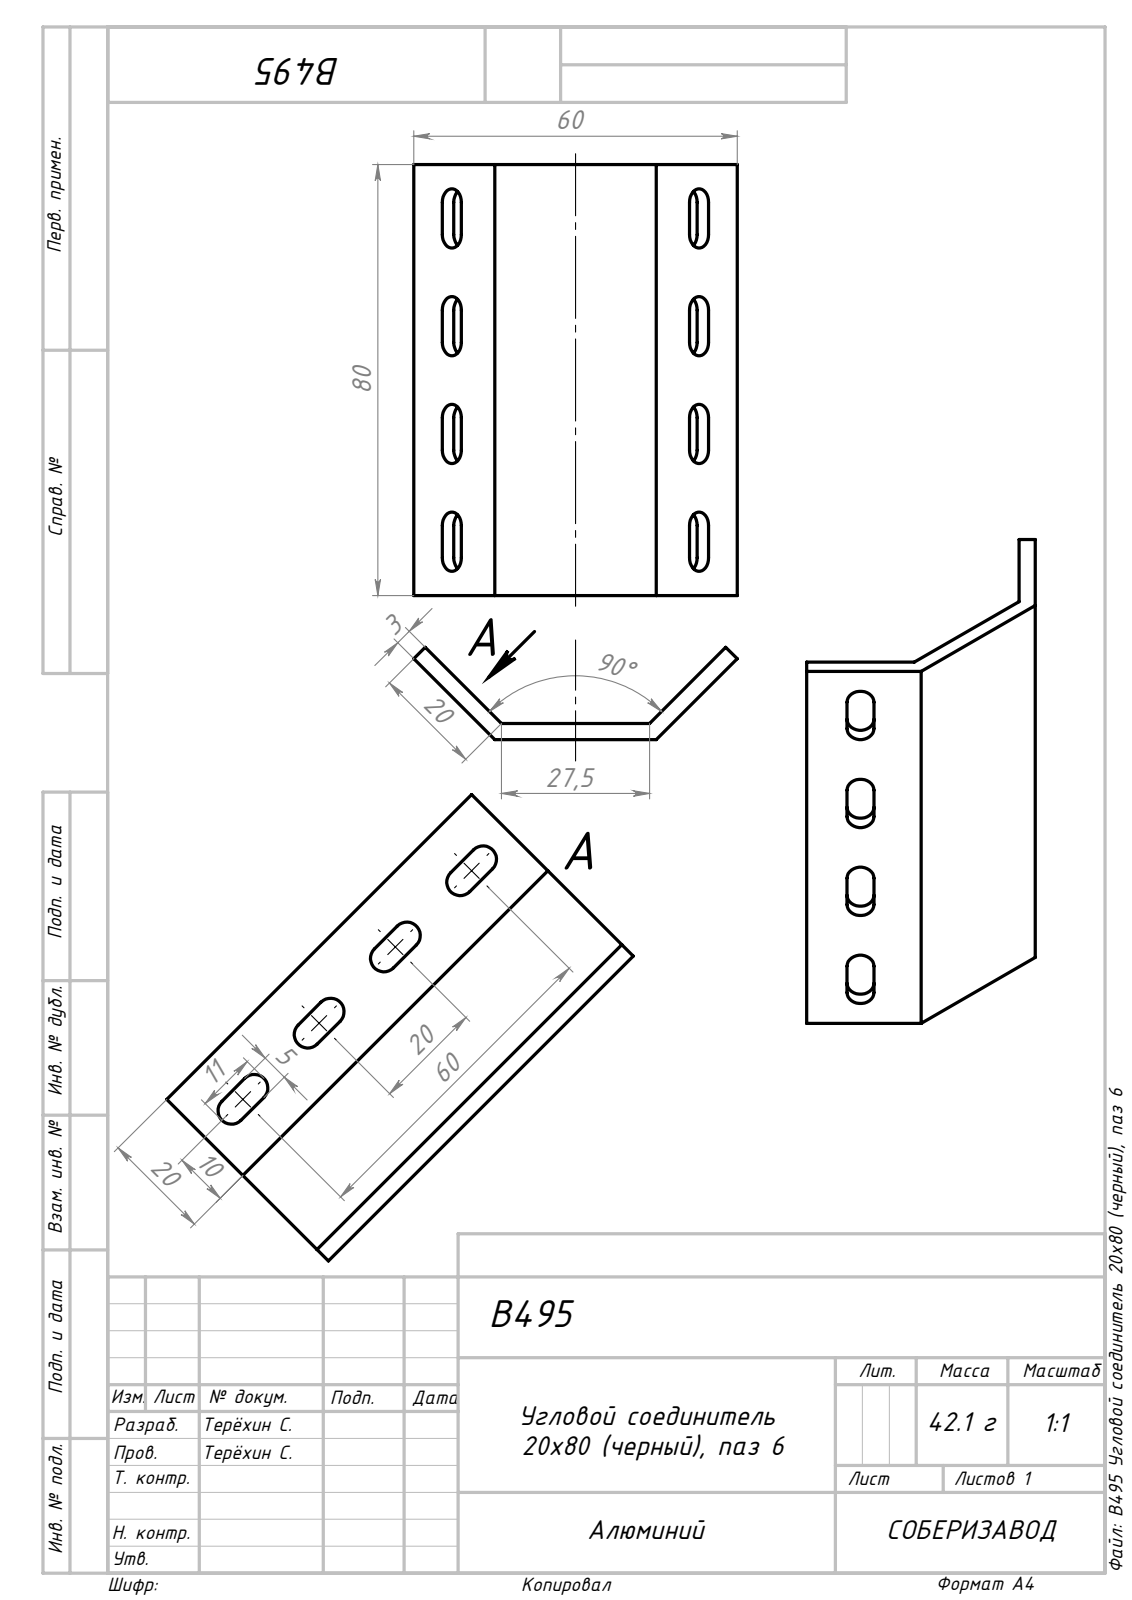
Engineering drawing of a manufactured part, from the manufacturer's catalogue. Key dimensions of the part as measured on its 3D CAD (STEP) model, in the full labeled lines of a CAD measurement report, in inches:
Part name (STEP PRODUCT): B495 Угловой соединитель 20x80 (черный), паз 6_00; Сборка2
STEP written by: SolidWorks 2022 (AUTOMOTIVE_DESIGN)
Units: inches
Bodies: 1 solid, 42 faces (26 planar, 16 cylindrical, 0 other)
Overall size (bounding box): 3.15 × 2.362 × 0.675
Volume: 0.952 in³ · Surface area: 18.54 in²
Partial cylindrical surfaces — rounded edges, fillets, slot ends (radius × count): R0.098 ×16
Main face-to-face distances: 0.118, 1.552, 1.67, 3.15, 0.492, 1.06, 1.178, 0.295, 0.197, 1.257
